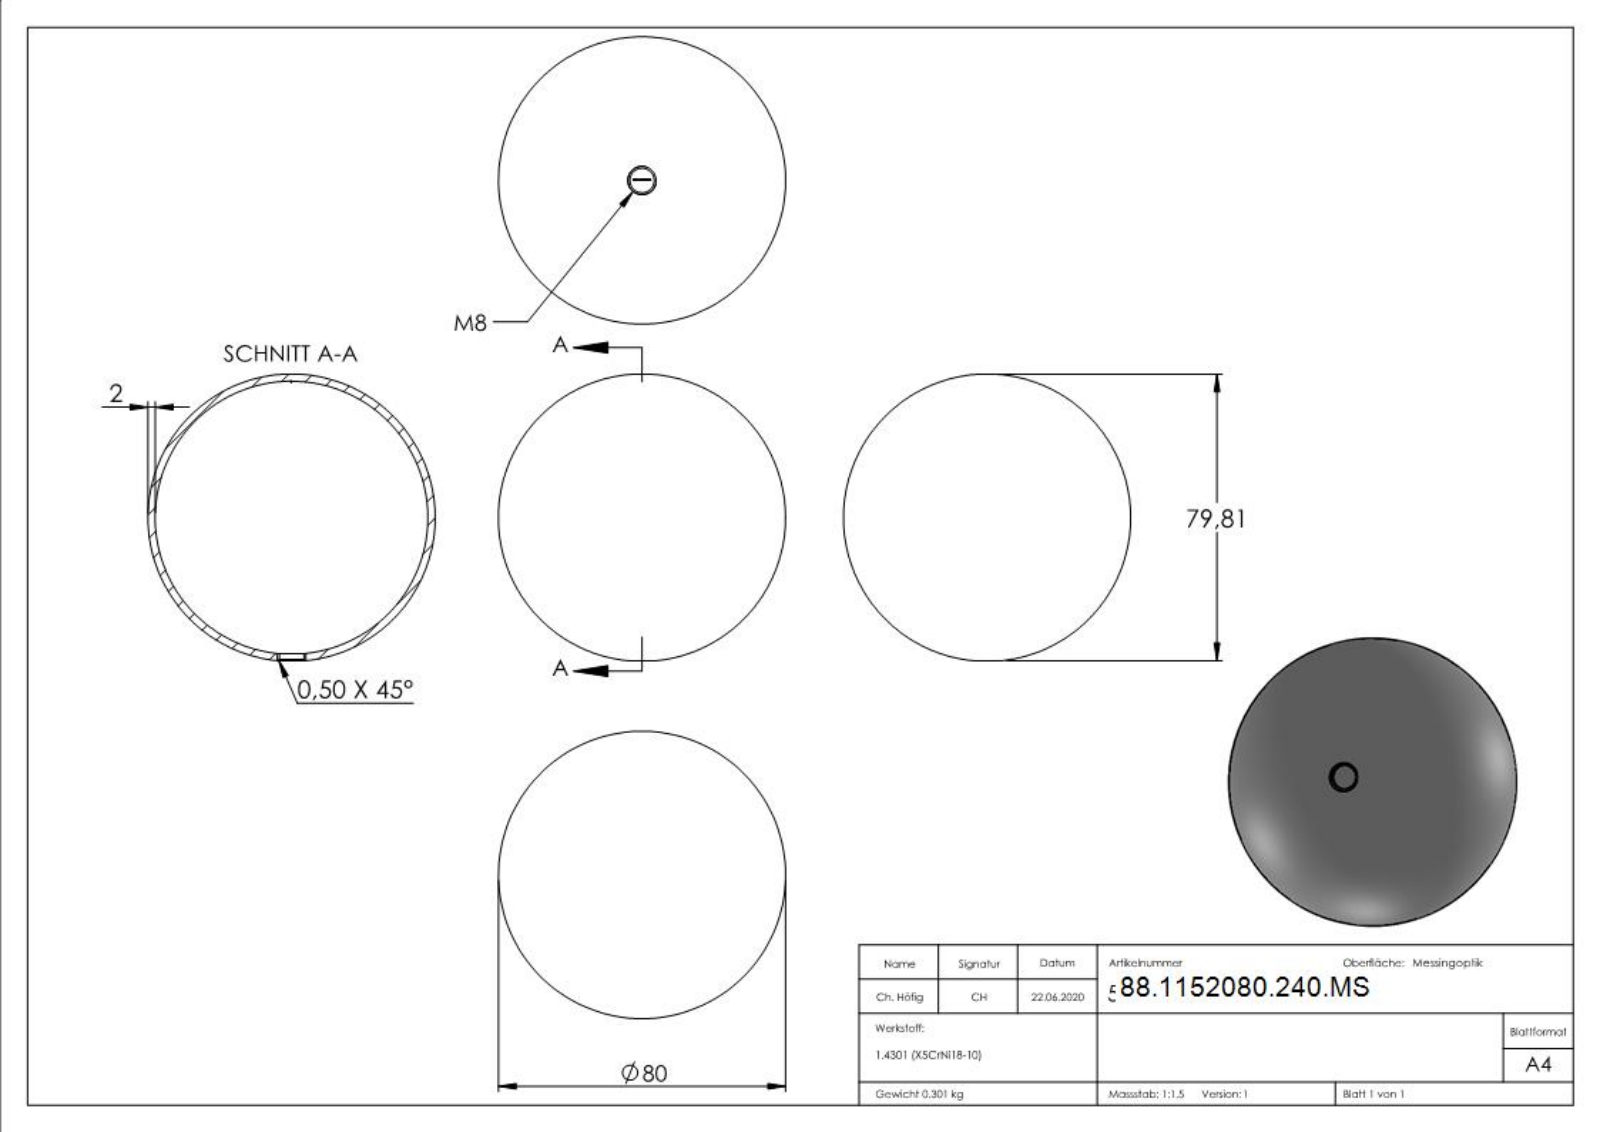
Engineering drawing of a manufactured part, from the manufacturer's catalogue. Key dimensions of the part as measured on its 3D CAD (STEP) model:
Part name (STEP PRODUCT): 52080-240-MS
STEP written by: SolidWorks 2015 (CONFIG_CONTROL_DESIGN)
Units: millimetres
Bodies: 1 solid, 268 faces (108 planar, 1 cylindrical, 159 other)
Overall size (bounding box): 80 × 80 × 79.81
Volume: 38 160 mm³ · Surface area: 38 218 mm²
Round holes (diameter × count): ⌀6.8 ×1
Main face-to-face distances: 0.31, 0.74, 3.32, 0.76, 0.68, 0.99, 0.45, 0.7, 0.77, 0.37
